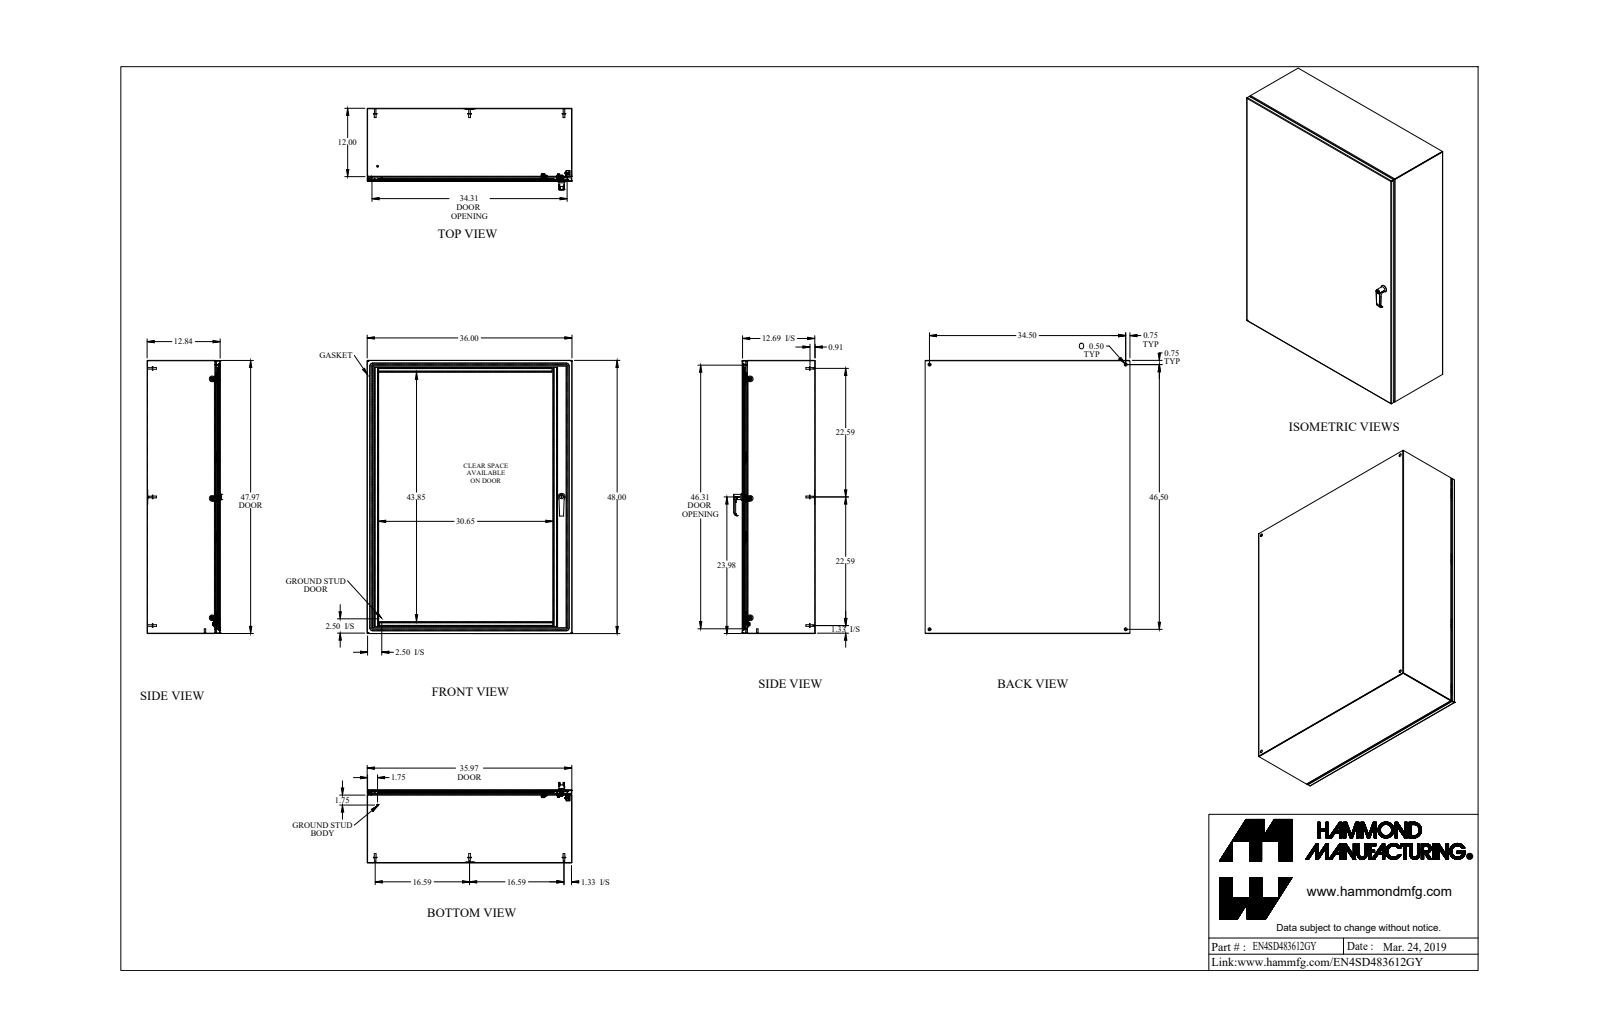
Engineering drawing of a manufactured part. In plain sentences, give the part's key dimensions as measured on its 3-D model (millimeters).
The part is named "EN4SD483612GY". Its 3-D file was written by "SolidWorks 2018 (AUTOMOTIVE_DESIGN)". It is 63 solids with 1719 faces: 757 planar, 632 cylindrical and 330 other. Overall it measures 1219.2 by 914.4 by 364.9 millimeters. Its volume is 7 451 000 cubic millimeters and its surface area 8 209 000 square millimeters. Round holes: 6 of diameter 4.5, 4 of diameter 5, 4 of diameter 12.7, 3 of diameter 6.4, 3 of diameter 6.7, 3 of diameter 10.5, 2 of diameter 6.1, 2 of diameter 6.5, 2 of diameter 8, 2 of diameter 10, 1 of diameter 4.4, 1 of diameter 6.1. Round bosses or shafts: 8 of diameter 8, 8 of diameter 6.9, 8 of diameter 6.4, 6 of diameter 15.9, 6 of diameter 9.5, 6 of diameter 4, 3 of diameter 25.4, 3 of diameter 15.9. Partial cylindrical surfaces (rounded edges, fillets, slot ends): 24 of radius 1.1, 24 of radius 2.1, 18 of radius 0.9, 18 of radius 2.7, 17 of radius 1.6, 15 of radius 0.8, 10 of radius 2.4, 9 of radius 0.4. The main face-to-face distances are 1.8, 324.2, 322.4, 326.1, 912.6, 910.7, 914.4, 1.8, 1215.5, 1217.4. The hole center spacings are 1066, 532.9, 533.1, 20, 533.4, 851, 876.3, 1181.1.
